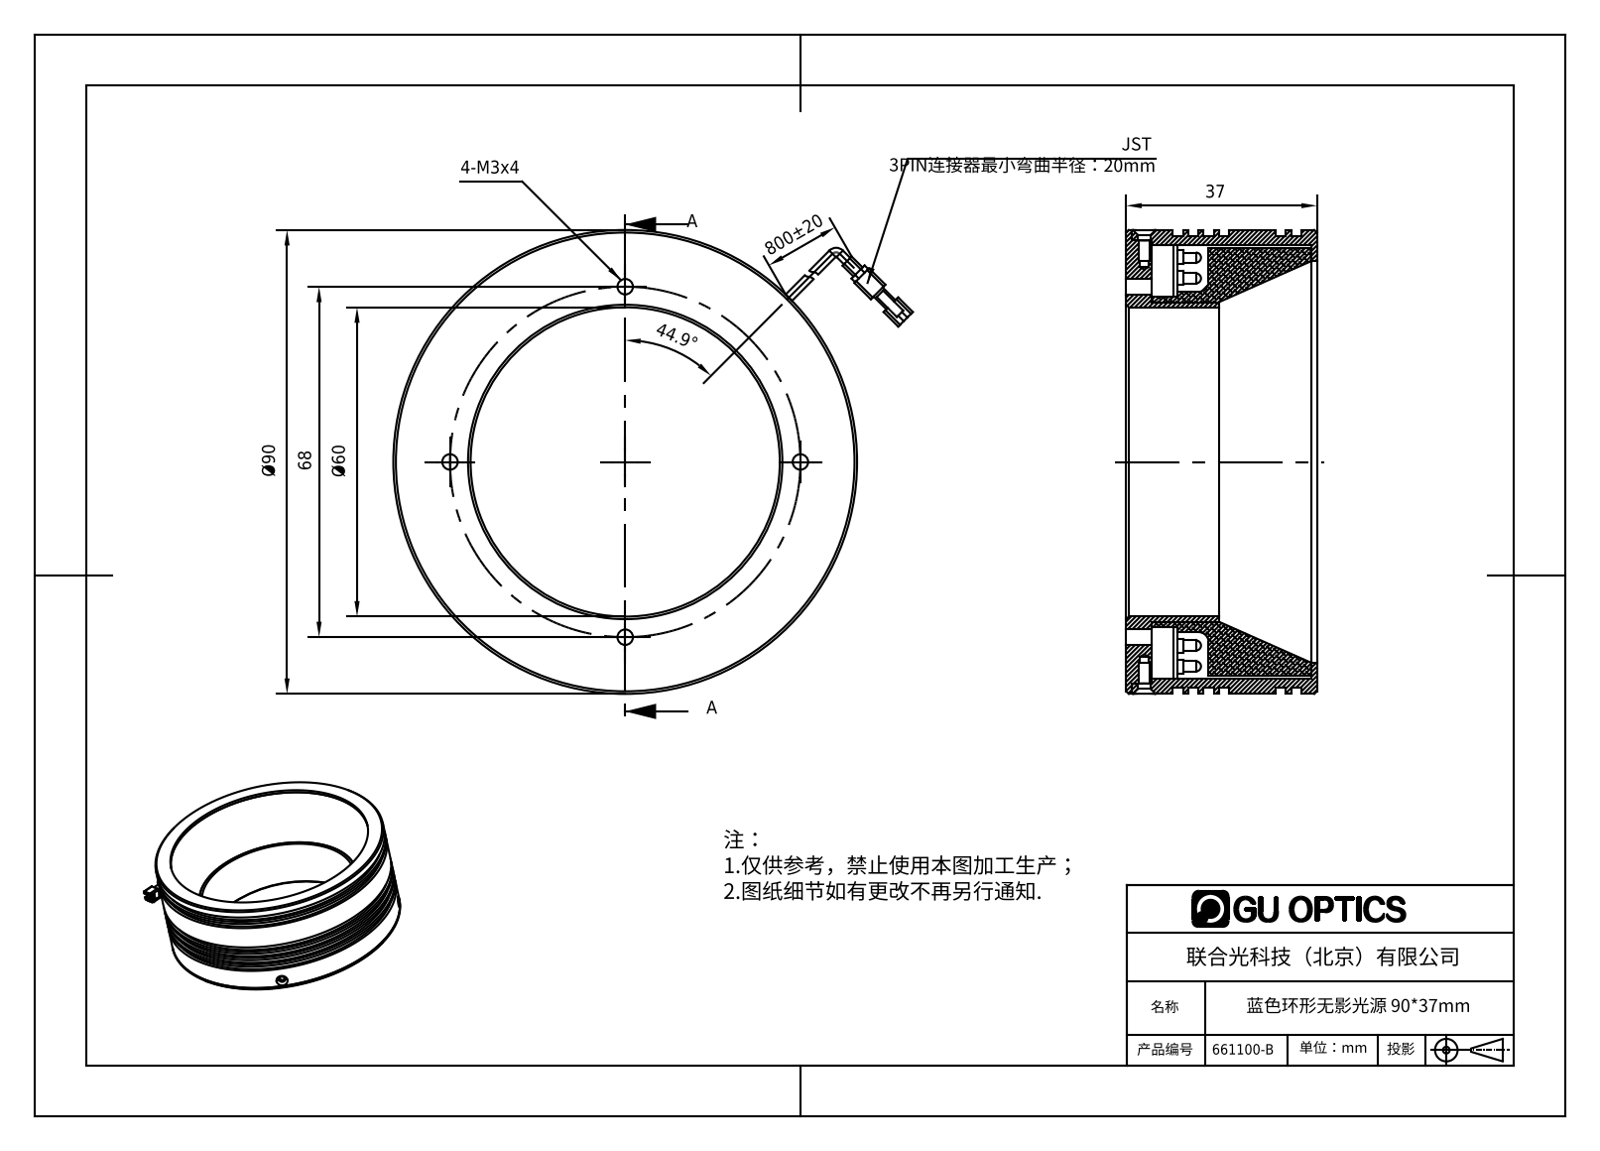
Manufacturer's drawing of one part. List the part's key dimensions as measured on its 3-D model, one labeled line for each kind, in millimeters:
Part name (STEP PRODUCT): 661100-B
STEP written by: SolidWorks 2016 (AUTOMOTIVE_DESIGN)
Units: millimetres
Bodies: 5 solids, 238 faces (87 planar, 121 cylindrical, 30 other)
Overall size (bounding box): 100.81 × 90 × 37
Volume: 78 932 mm³ · Surface area: 58 794 mm²
Round holes (diameter × count): ⌀3 ×4, ⌀1.6 ×2, ⌀2 ×2, ⌀2.4 ×2, ⌀3.8 ×1, ⌀60 ×1, ⌀62 ×1, ⌀78 ×1, ⌀84 ×1
Round bosses / shafts (diameter × count): ⌀1.75 ×2, ⌀90 ×1, ⌀87.6 ×1, ⌀86 ×1, ⌀83 ×1, ⌀66 ×1, ⌀64 ×1
Partial cylindrical surfaces — rounded edges, fillets, slot ends (radius × count): R0.5 ×8, R1 ×4, R6 ×1
Main face-to-face distances: 5, 1, 2, 4, 16, 11, 3, 15, 20, 17
Hole centre spacings: 34, 48.08, 68
